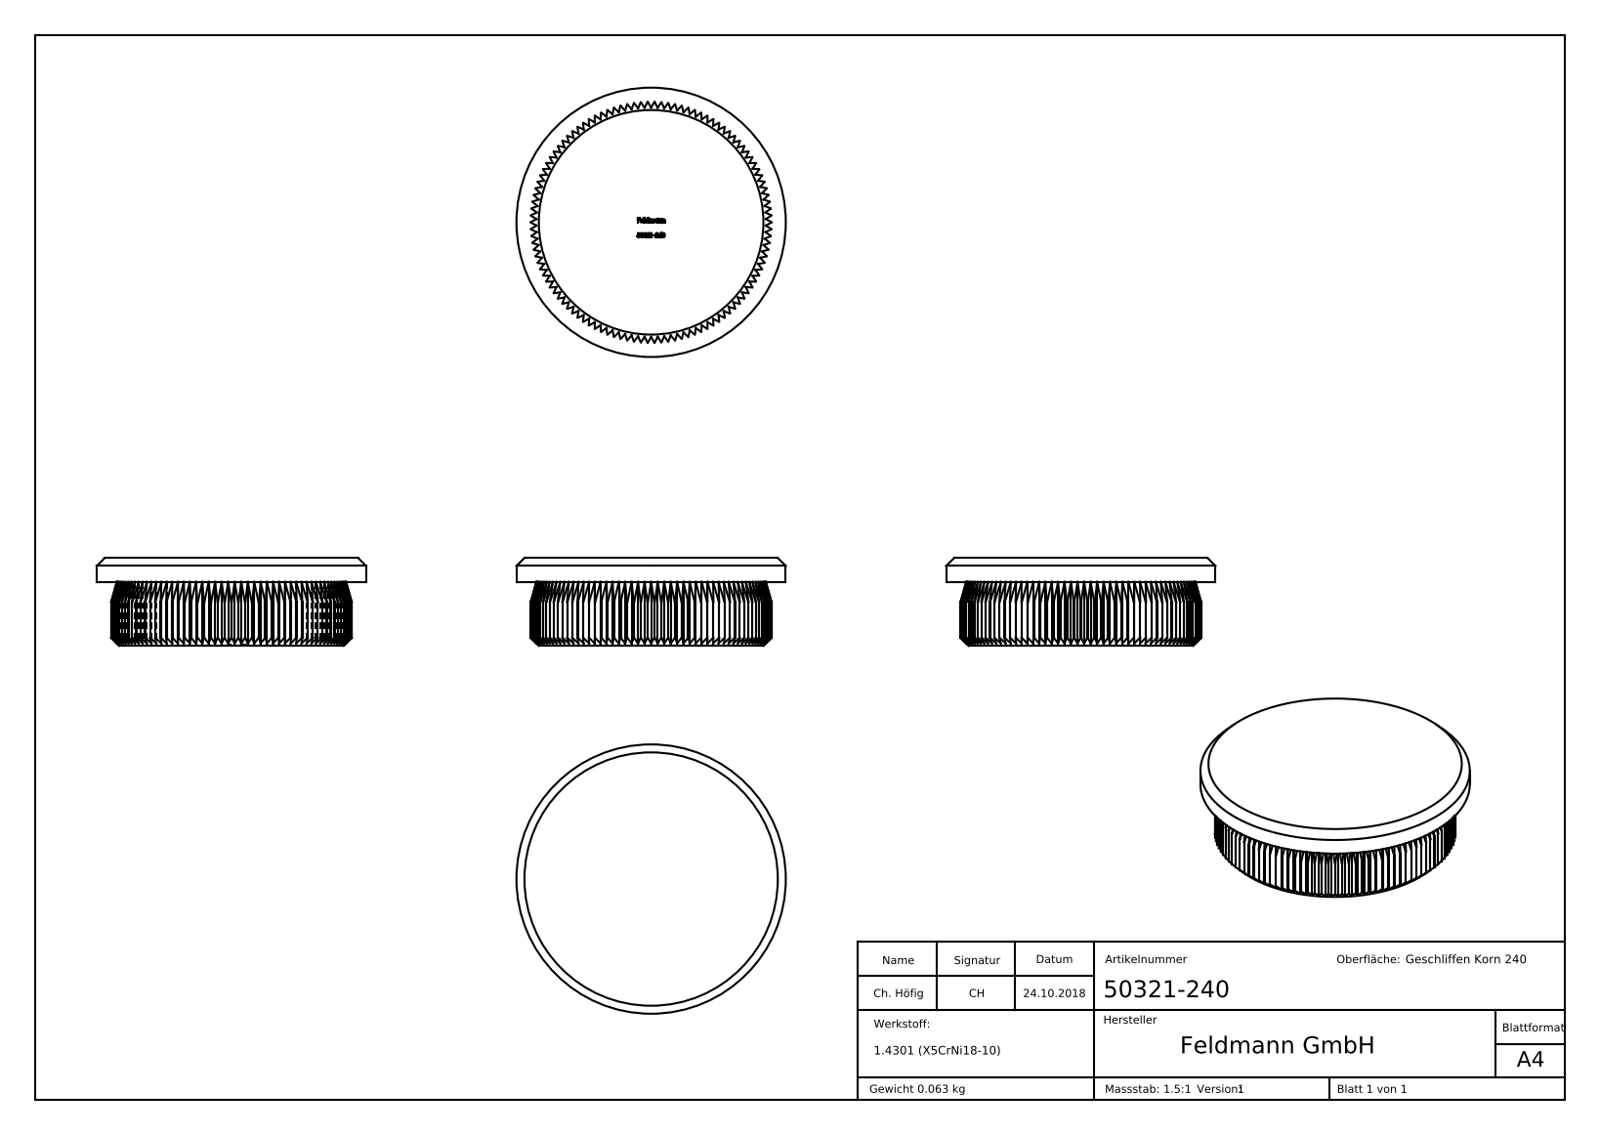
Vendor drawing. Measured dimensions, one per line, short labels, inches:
name: 50321-240
written by: SolidWorks 2015 (CONFIG_CONTROL_DESIGN)
unit: in
bodies: 1 solid, 702 faces (361 planar, 112 cylindrical, 229 other)
size: 1.327 × 1.327 × 0.433
volume: 0.489 in³; area: 5.165 in²
bosses: 1× ⌀1.327
rounds: 1× R0.593
face distances: 0.433, 0.565, 0.565, 0.315, 0.118, 0.311, 0.429, 0.065, 0.072, 0.026
